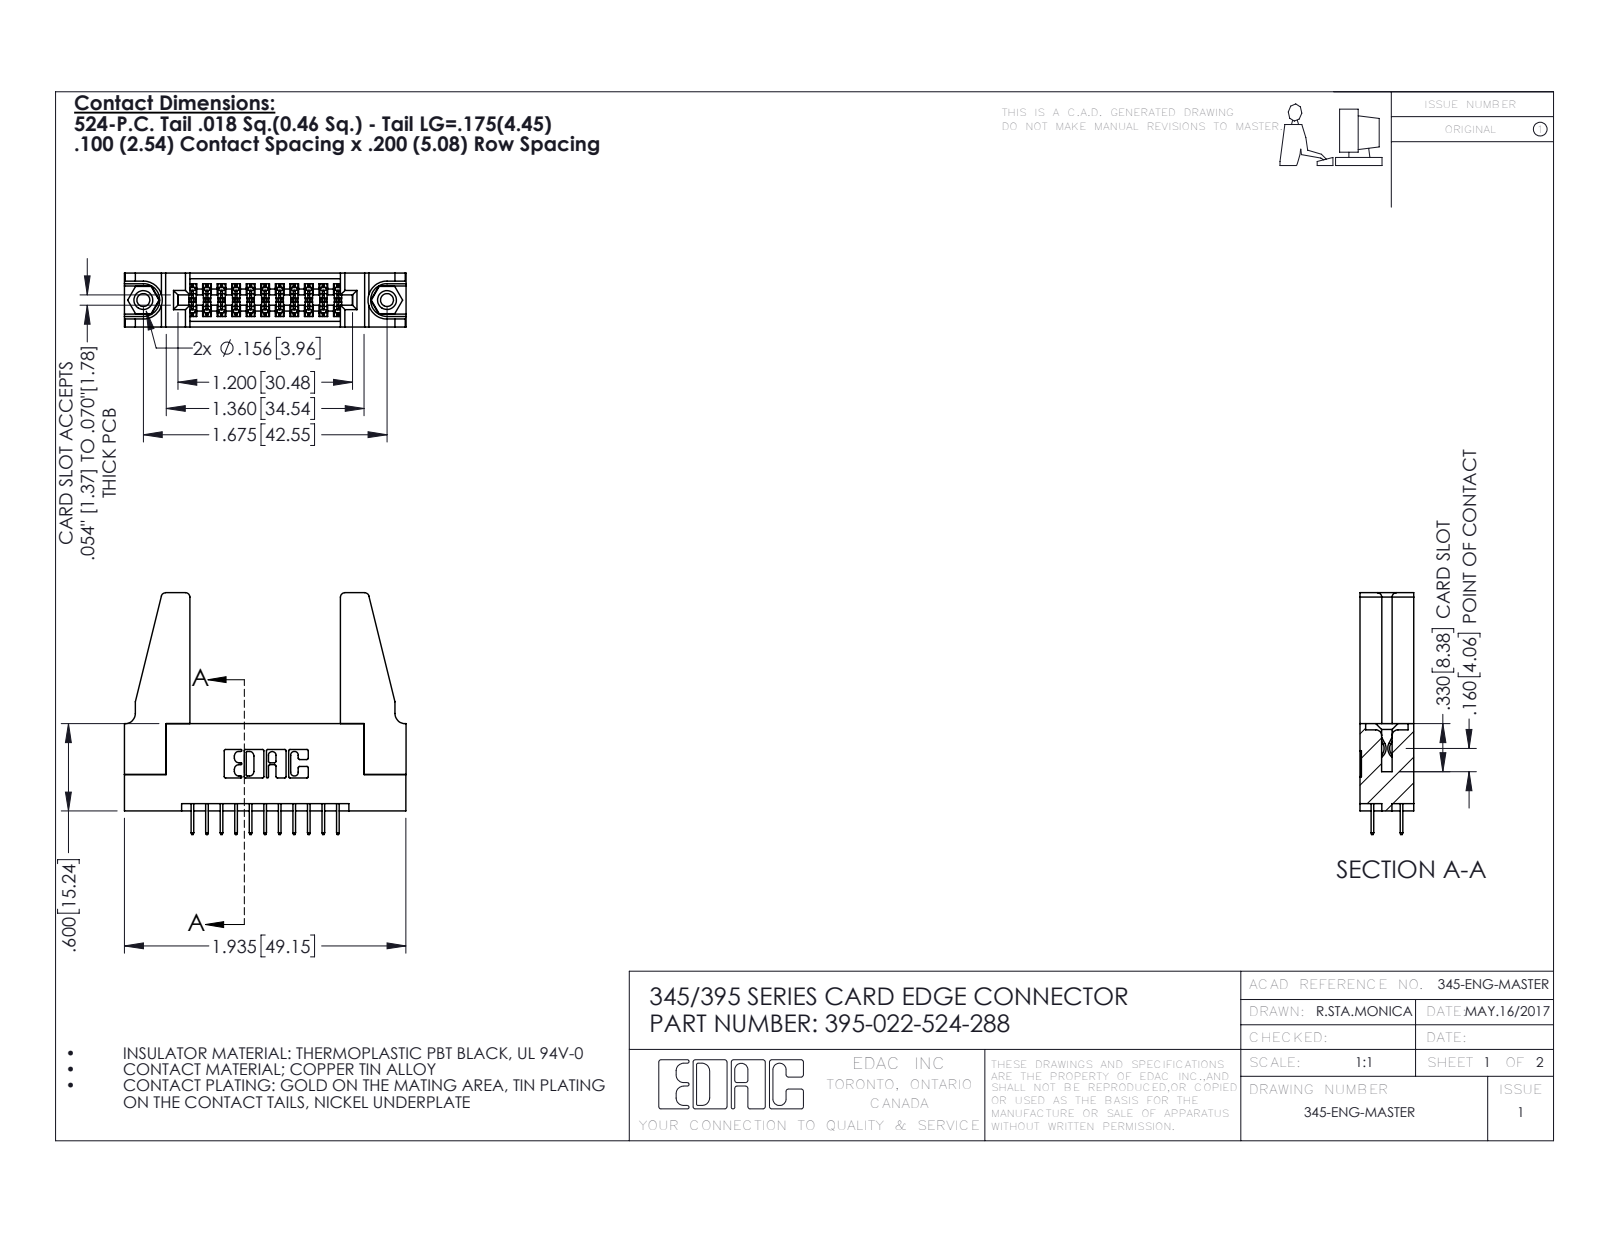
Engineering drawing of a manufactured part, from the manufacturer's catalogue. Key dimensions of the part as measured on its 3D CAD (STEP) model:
Part name (STEP PRODUCT): 345-292-001_345-293-124; 345 Part_Flush Mounting Lugs - 0.156 Dia-TH; 345-250-001_345-250-001-102; 345-220-078_345-220-088 (+1 more)
STEP written by: SolidWorks 2016 (CONFIG_CONTROL_DESIGN)
Units: inches
Bodies: 27 solids, 1438 faces (1010 planar, 412 cylindrical, 16 other)
Overall size (bounding box): 1.936 × 1.662 × 0.37
Volume: 0.47 in³ · Surface area: 13.98 in²
Round holes (diameter × count): ⌀0.089 ×2, ⌀0.125 ×2, ⌀0.156 ×2, ⌀0.064 ×1
Round bosses / shafts (diameter × count): ⌀0.155 ×2
Partial cylindrical surfaces — rounded edges, fillets, slot ends (radius × count): R0.006 ×33, R0.01 ×22, R0.03 ×8, R0.007 ×6, R0.031 ×6, R0.026 ×3, R0.014 ×2, R0.019 ×2
Main face-to-face distances: 0.37, 0.072, 0.298, 0.2, 0.225, 0.098, 0.272, 0.025, 0.148, 0.15
Hole centre spacings: 0.27, 1.443, 1.675
